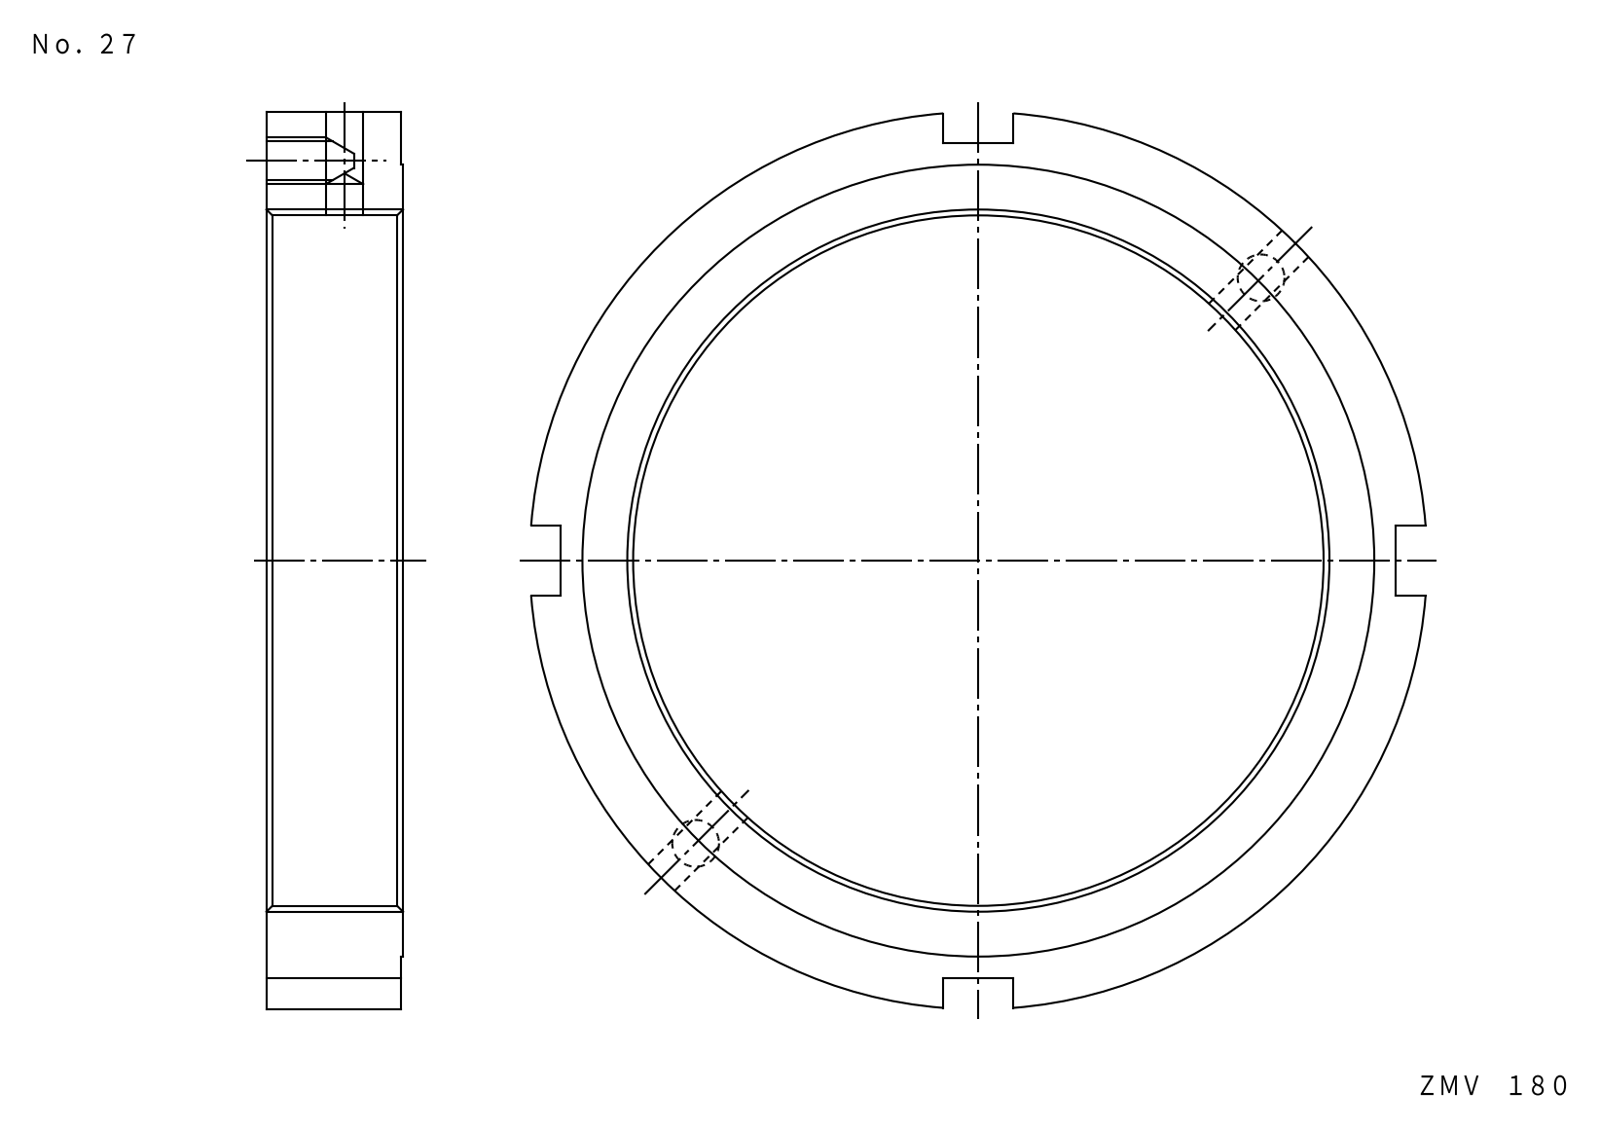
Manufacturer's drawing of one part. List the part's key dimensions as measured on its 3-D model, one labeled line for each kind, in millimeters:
Part name (STEP PRODUCT): FKD ZMV180
STEP written by: Autodesk Inventor LT (CONFIG_CONTROL_DESIGN)
Units: millimetres
Bodies: 1 solid, 29 faces (15 planar, 10 cylindrical, 4 other)
Overall size (bounding box): 229.29 × 229.29 × 35
Volume: 533 160 mm³ · Surface area: 80 156 mm²
Round holes (diameter × count): ⌀9.6 ×2, ⌀10.11 ×2, ⌀180 ×1
Round bosses / shafts (diameter × count): ⌀230 ×1, ⌀203 ×1
Main face-to-face distances: 34.5, 0.5, 35, 98, 116, 214, 18
Hole centre spacings: 102.5, 205
